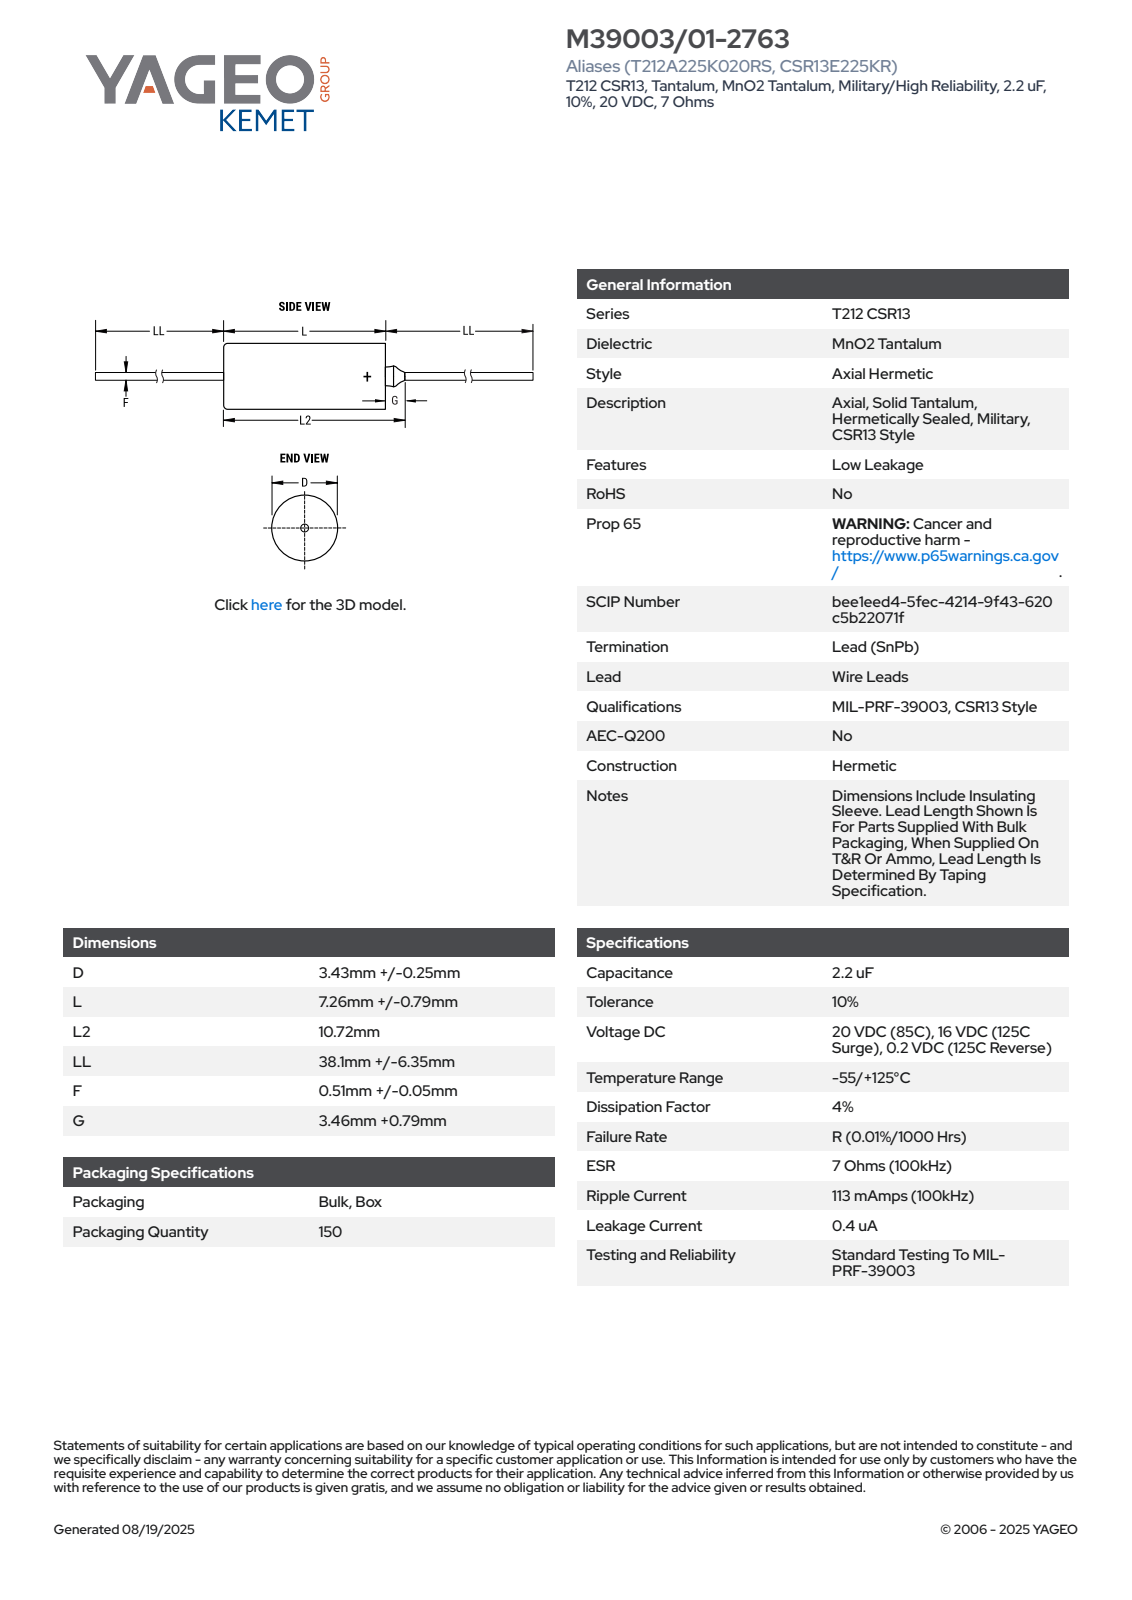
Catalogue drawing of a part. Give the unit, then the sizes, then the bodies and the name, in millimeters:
Units: millimetres
Overall size (bounding box): 96.95 × 3.68 × 3.68
Round holes (diameter × count): ⌀3.28 ×1
Round bosses / shafts (diameter × count): ⌀3.68 ×1, ⌀1.33 ×1, ⌀1.3 ×1, ⌀0.56 ×1
Partial cylindrical surfaces — rounded edges, fillets, slot ends (radius × count): R1.83 ×1
Main face-to-face distances: 5.88, 7.88, 2, 44.45, 52.5, 44.62, 50.5, 96.95, 52.33, 46.45
Volume: 94 mm³ · Surface area: 302 mm²
Bodies: 1 solid, 99 faces (30 planar, 30 cylindrical, 39 other)
Part name (STEP PRODUCT): CTAM_AHTWG_D3.68L8.05L210.72LL44.45F0.56G4.25
STEP written by: SolidWorks 2014 (AUTOMOTIVE_DESIGN)
